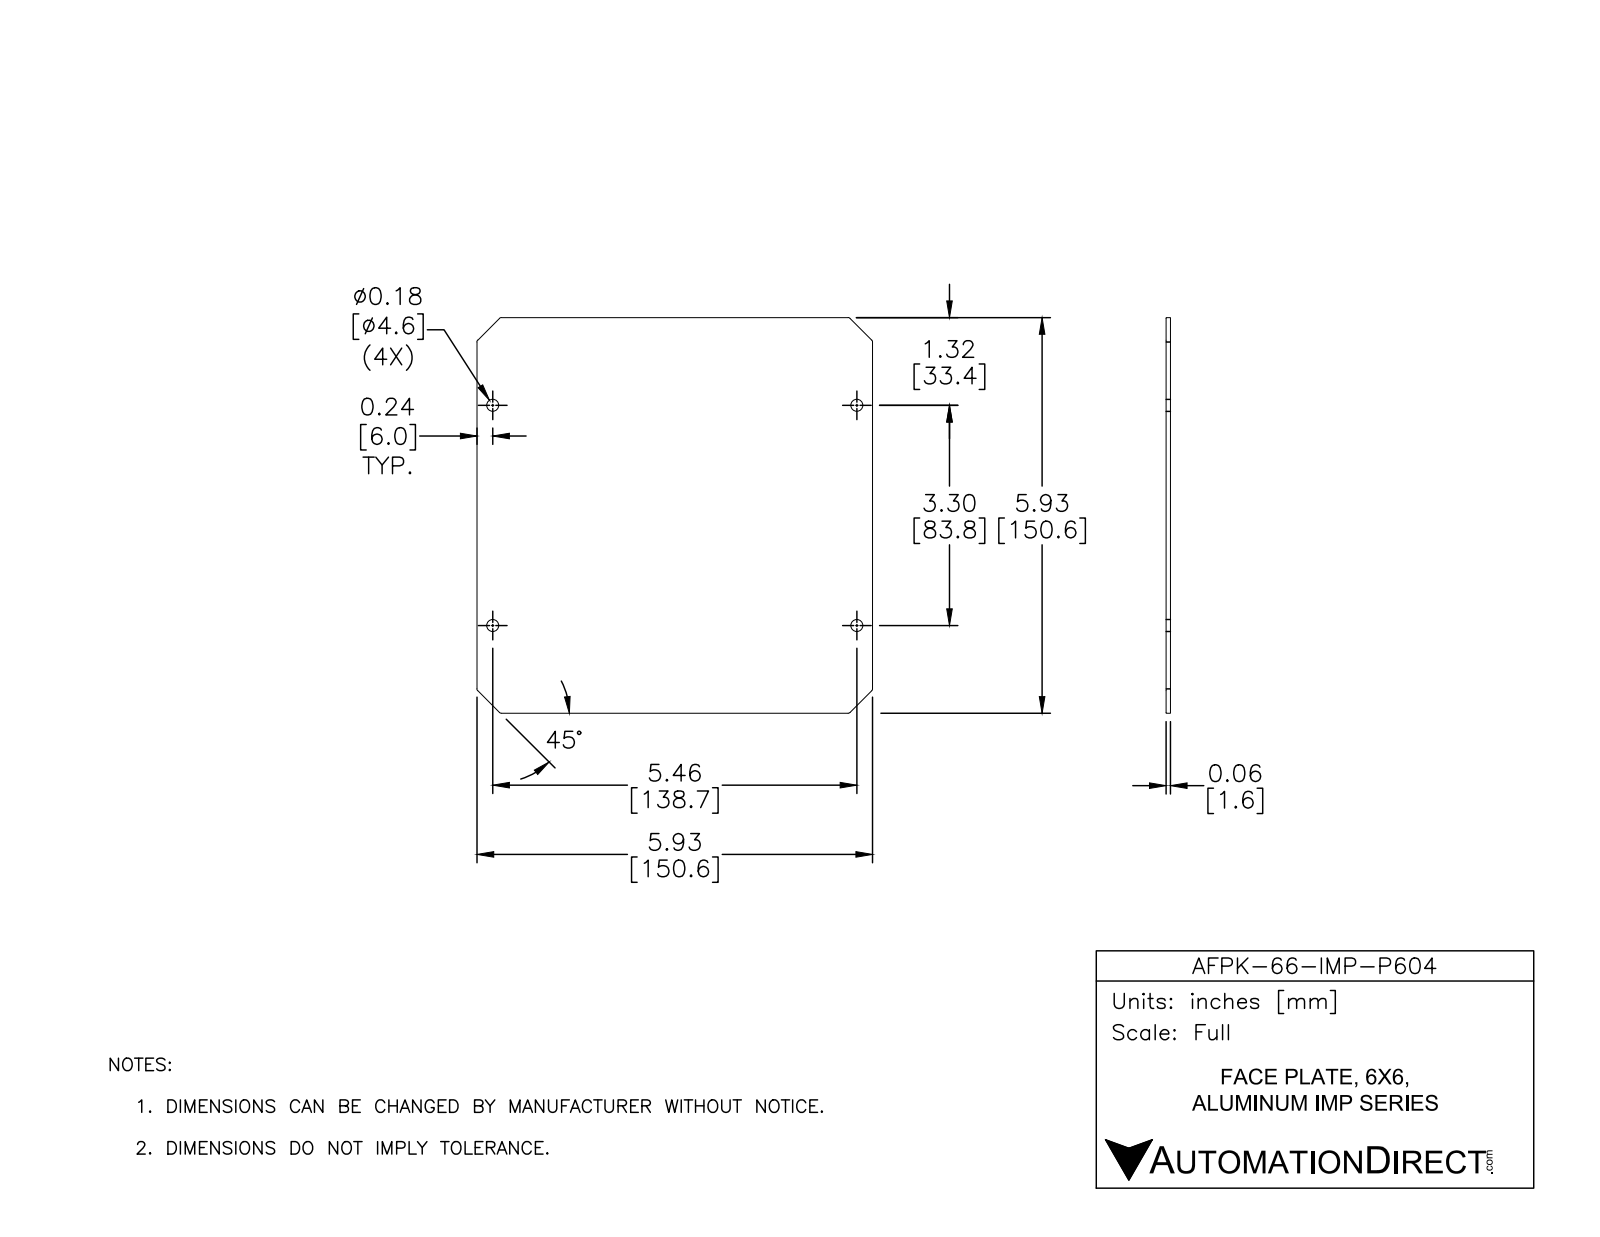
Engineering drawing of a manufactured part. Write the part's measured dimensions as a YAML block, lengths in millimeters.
part_name: "AFPK66-IMP-P604"
step_written_by: "SolidWorks 2016 (AUTOMOTIVE_DESIGN)"
units: millimeters
bodies: {solids: 1, faces: 26, planar: 10, cylindrical: 16, other: 0}
overall_size: [150.6, 150.6, 1.6]
volume: 36580
surface_area: 45970
round_holes:
  - {diameter: 4.6, count: 4}
partial_cylinders:
  - {radius: 1, count: 8}
face_to_face_distances: [1.6, 150.6, 200.4]
hole_center_spacings: [83.8, 138.7, 162.1]
